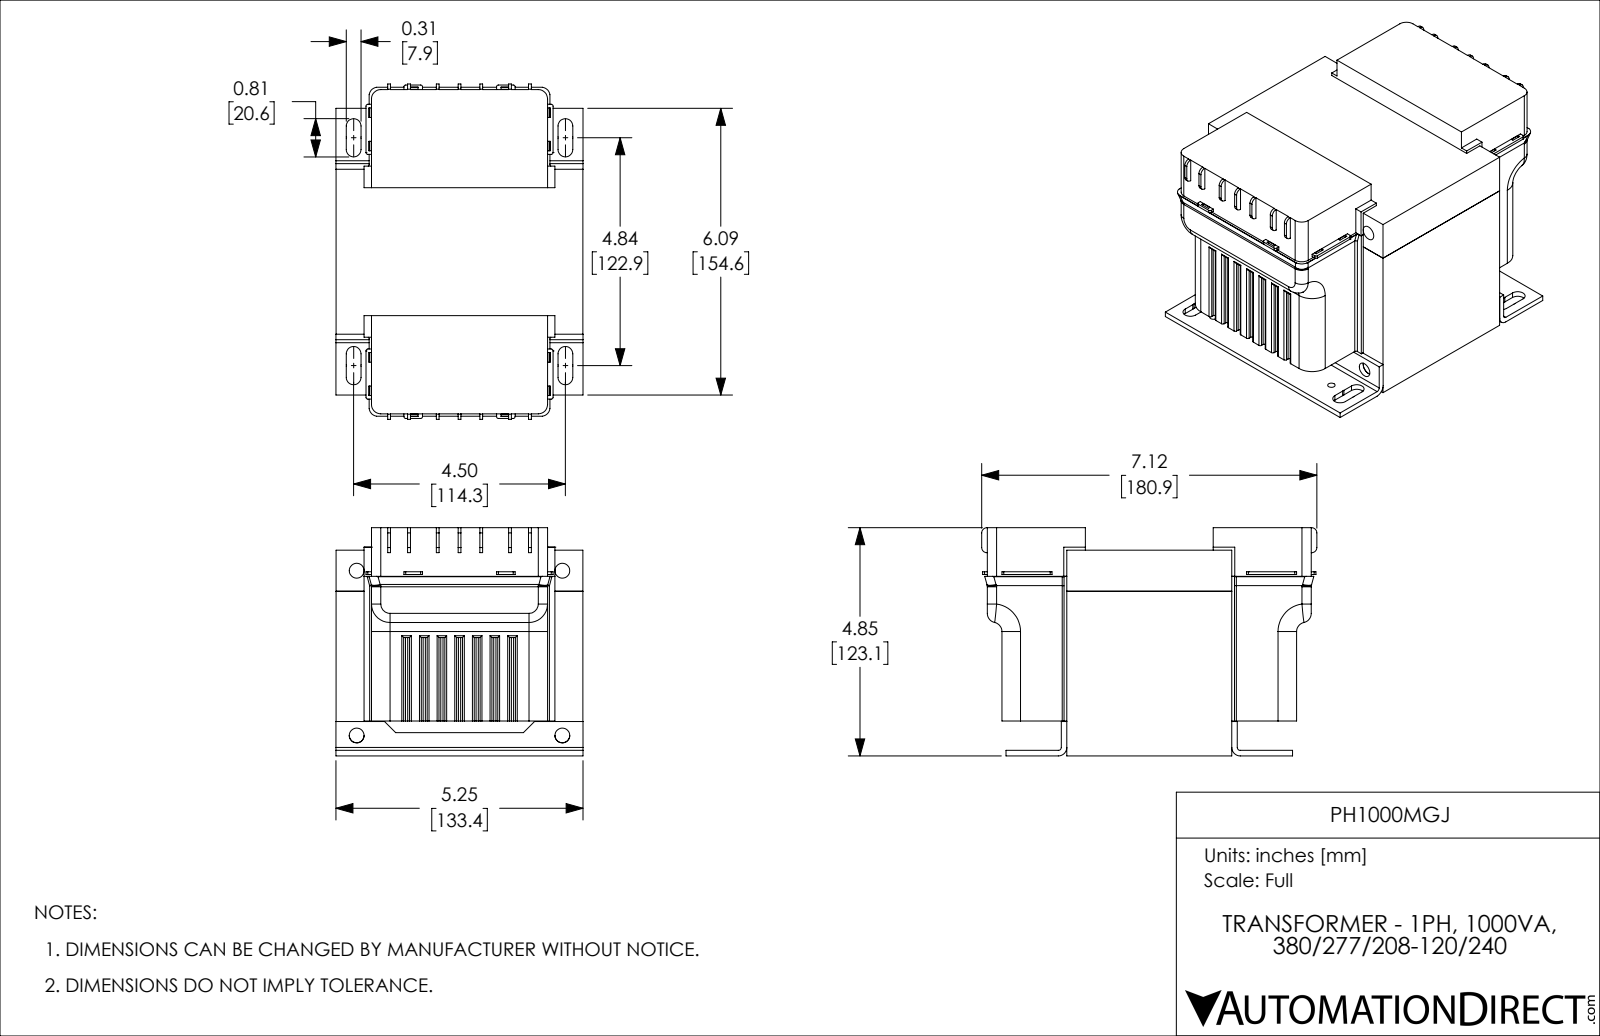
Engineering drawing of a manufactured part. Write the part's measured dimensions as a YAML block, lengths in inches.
part_name: "PH1000MGJ"
step_written_by: "SolidWorks 2018 (AUTOMOTIVE_DESIGN)"
units: inches
bodies: {solids: 9, faces: 546, planar: 328, cylindrical: 198, other: 20}
overall_size: [7.121, 5.25, 4.847]
volume: 113.3
surface_area: 389.4
round_holes:
  - {diameter: 0.315, count: 6}
  - {diameter: 0.157, count: 4}
partial_cylinders:
  - {radius: 0.039, count: 82}
  - {radius: 0.197, count: 16}
  - {radius: 0.156, count: 8}
  - {radius: 0.11, count: 4}
  - {radius: 0.157, count: 4}
  - {radius: 0.394, count: 4}
  - {radius: 0.062, count: 2}
  - {radius: 0.181, count: 2}
face_to_face_distances: [0.874, 3.496, 4.37, 3.504, 1.748, 3.814, 0.318, 2.622, 0.556, 0.752]
hole_center_spacings: [4.37, 3.496, 3.499, 3.543, 4.907, 5.596, 5.598, 6.053]
